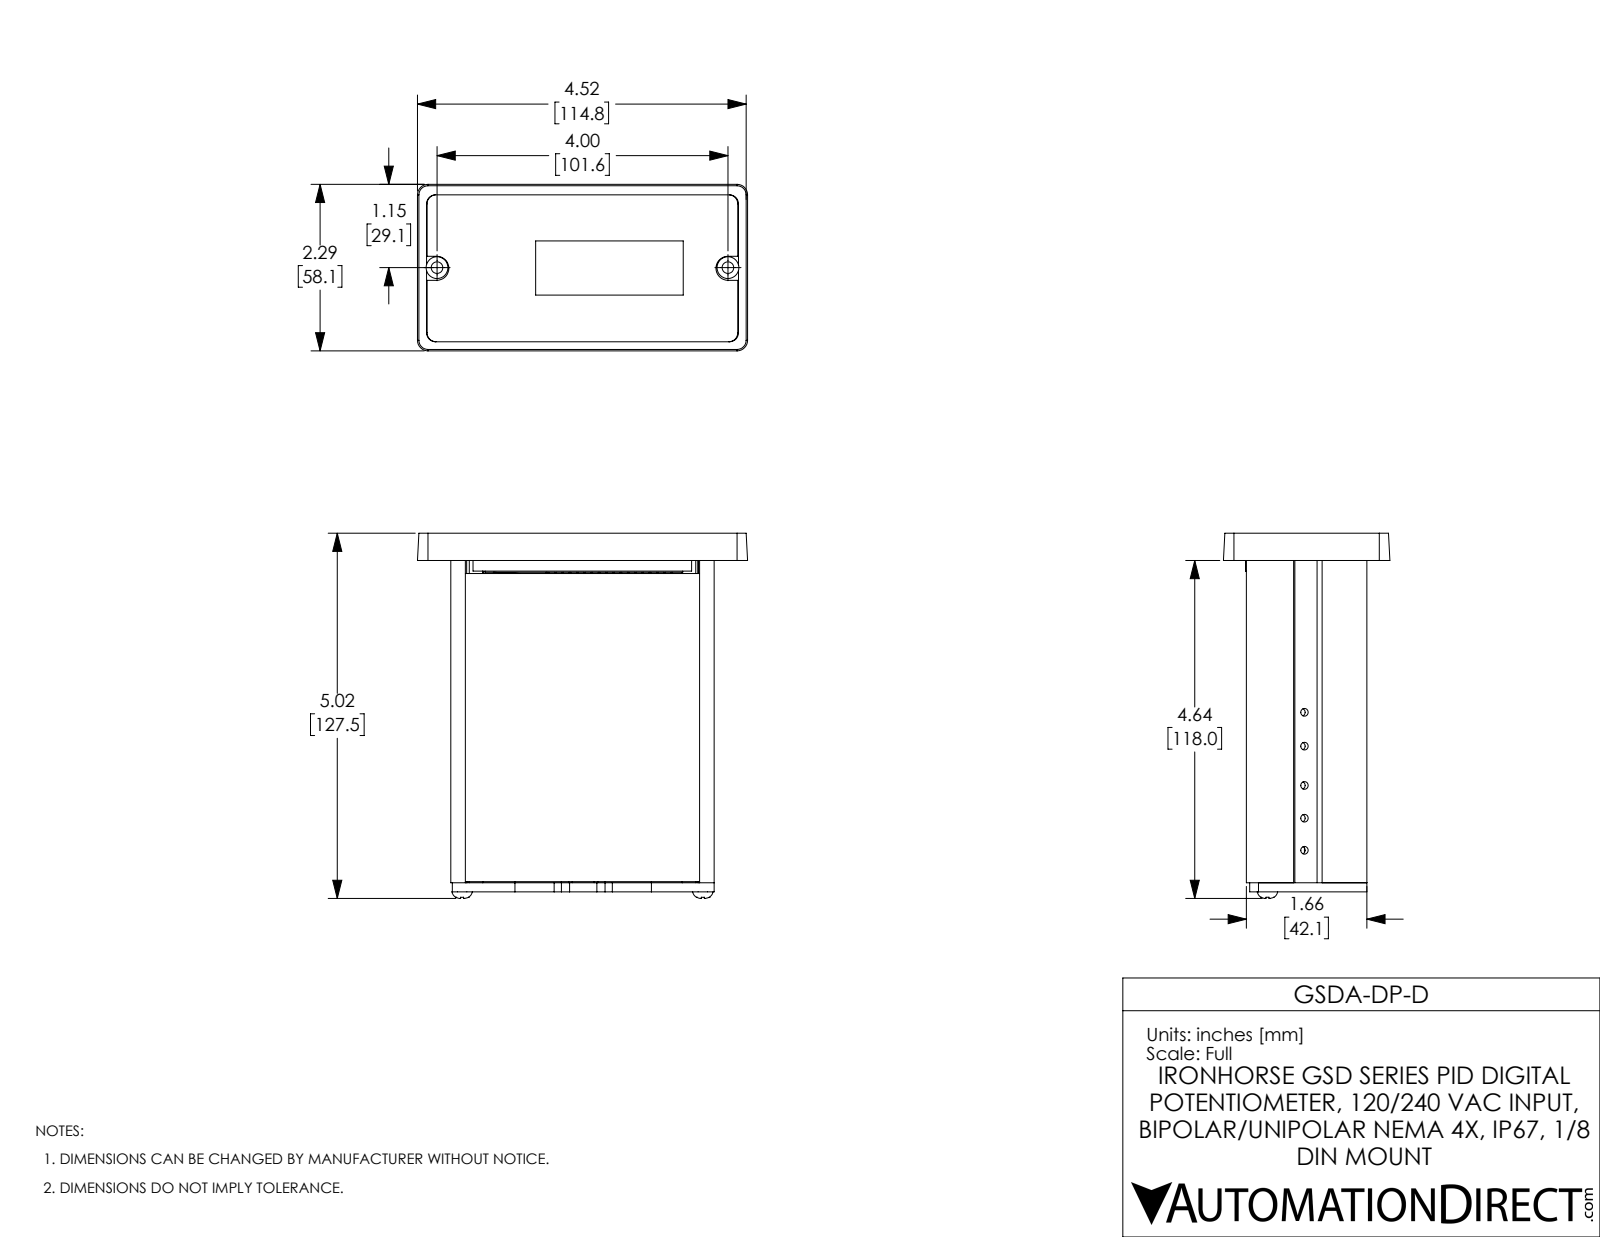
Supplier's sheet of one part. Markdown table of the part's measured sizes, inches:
| quantity | value |
| --- | --- |
| part name | GSDA-DP-D |
| STEP written by | SolidWorks 2017 (AUTOMOTIVE_DESIGN) |
| units | inches |
| bodies | 15 solids, 1227 faces (759 planar, 447 cylindrical, 21 other) |
| overall size | 5.019 × 4.539 × 2.289 |
| volume | 9.053 in³ |
| surface area | 219 in² |
| round holes (diameter × count) | 0.033 × 36, 0.035 × 13, 0.157 × 12, 0.02 × 6, 0.059 × 6, 0.147 × 6, 0.16 × 6, 0.106 × 5, 0.12 × 4, 0.285 × 4, 0.016 × 3, 0.112 × 3 |
| round bosses / shafts (diameter × count) | 0.02 × 36, 0.247 × 3, 0.134 × 2 |
| partial cylindrical surfaces (radius × count) | 0.05 × 18, 0.039 × 16, 0.125 × 12, 0.126 × 10, 0.025 × 7, 0.016 × 4, 0.035 × 4, 0.045 × 4 |
| main face-to-face distances | 0.1, 1.521, 0.045, 1.566, 1.421, 1.466, 0.031, 1.313, 0.209, 0.178 |
| hole center spacings | 0.197, 0.394, 0.591, 0.787, 0.984, 1.181, 0.1, 0.2 |
